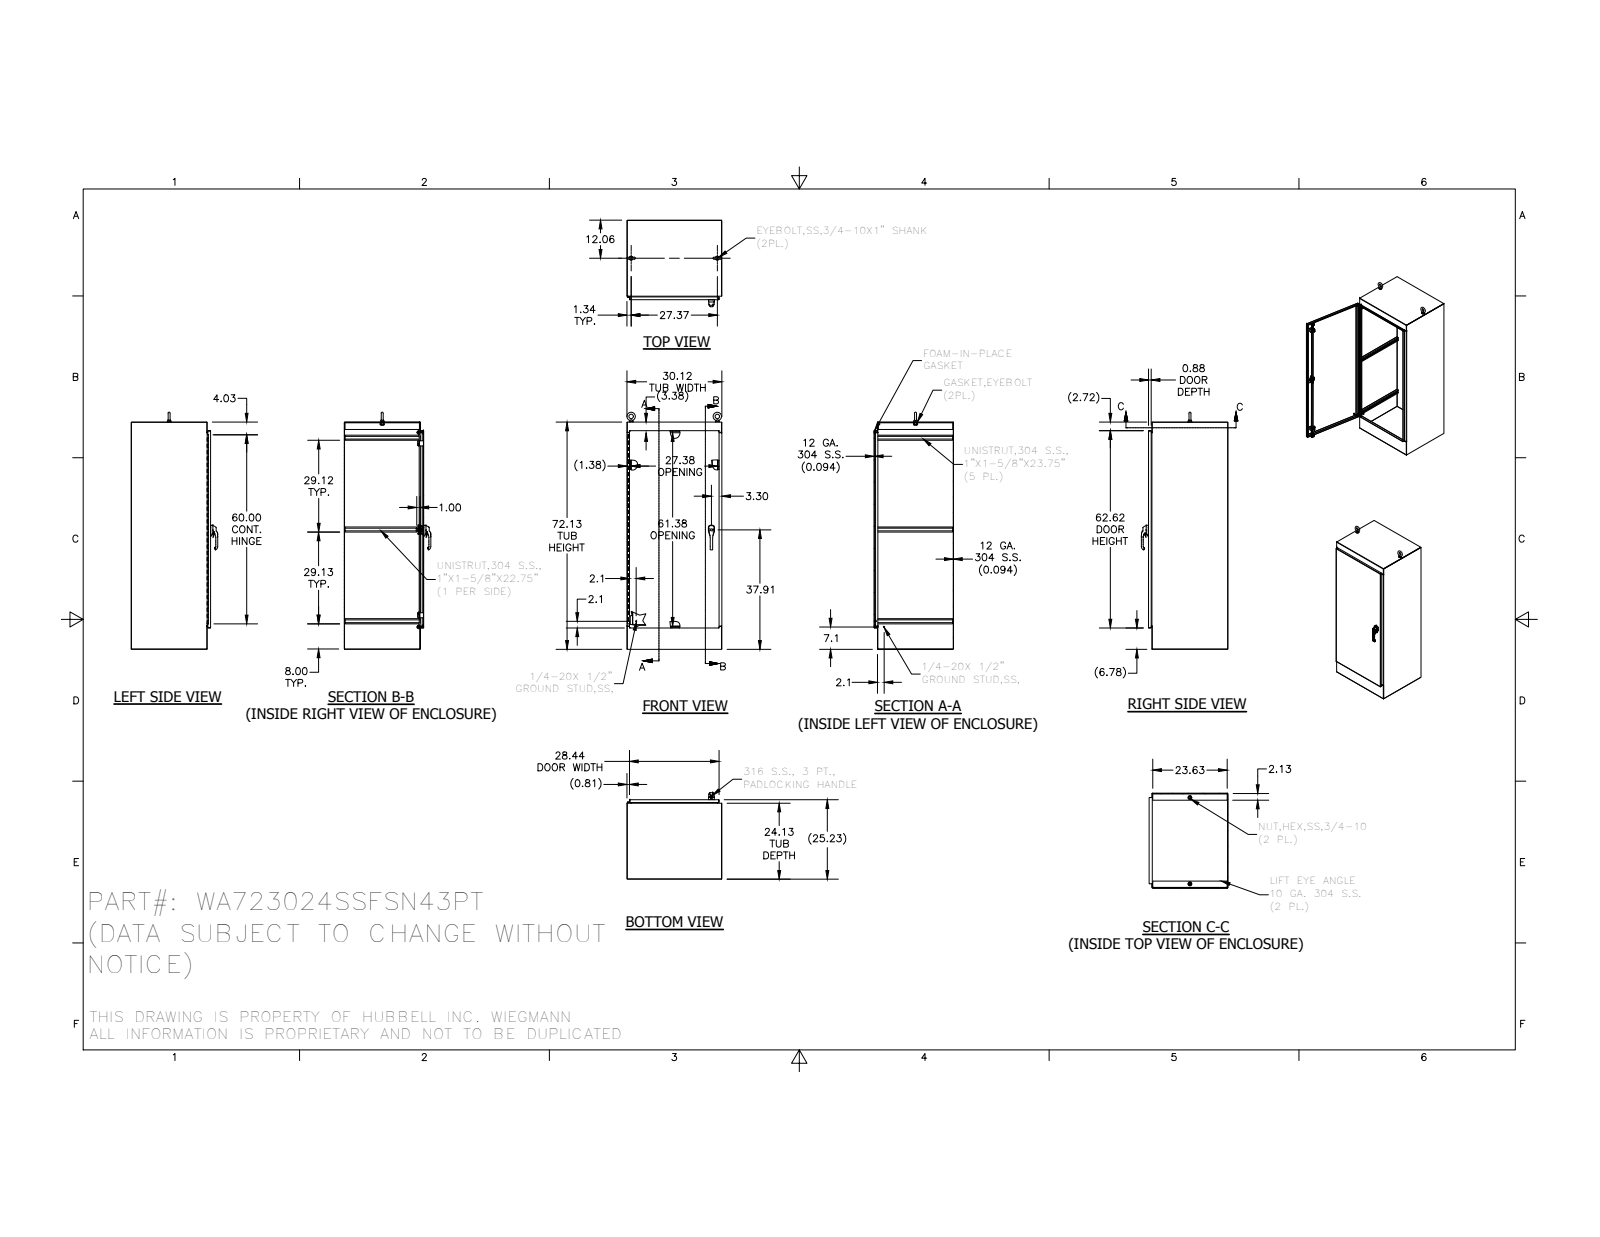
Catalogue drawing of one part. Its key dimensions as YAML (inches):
part_name: "1091-903_AF0; 37029; HFW31234; PLASTIC-ROLLER-CAM_AF0_ASM (+8 more)"
step_written_by: "SolidWorks 2014 (AUTOMOTIVE_DESIGN)"
units: inches
bodies: {solids: 66, faces: 3475, planar: 1228, cylindrical: 1307, other: 940}
overall_size: [75.248, 30.125, 27.476]
volume: 1064
surface_area: 22039
round_holes:
  - {diameter: 0.262, count: 8}
  - {diameter: 0.375, count: 8}
  - {diameter: 0.187, count: 4}
  - {diameter: 0.25, count: 4}
  - {diameter: 0.213, count: 3}
  - {diameter: 0.28, count: 3}
  - {diameter: 0.241, count: 2}
  - {diameter: 0.252, count: 2}
  - {diameter: 0.315, count: 2}
  - {diameter: 0.4, count: 2}
  - {diameter: 0.402, count: 2}
  - {diameter: 0.413, count: 2}
round_bosses_or_shafts:
  - {diameter: 1, count: 4}
  - {diameter: 0.236, count: 3}
  - {diameter: 1.25, count: 2}
  - {diameter: 1.12, count: 2}
  - {diameter: 0.75, count: 2}
  - {diameter: 0.563, count: 2}
  - {diameter: 0.533, count: 2}
  - {diameter: 0.531, count: 2}
partial_cylinders:
  - {radius: 0.02, count: 180}
  - {radius: 0.012, count: 107}
  - {radius: 0.125, count: 26}
  - {radius: 0.019, count: 23}
  - {radius: 0.05, count: 19}
  - {radius: 0.031, count: 17}
  - {radius: 0.079, count: 14}
  - {radius: 0.125, count: 13}
face_to_face_distances: [0.094, 25.133, 30.031, 25.039, 29.937, 25.227, 30.125, 72.031, 24.031, 1.102]
hole_center_spacings: [6.667, 20, 0.38, 0.76, 2.763, 13.333, 26.667, 31.665]
